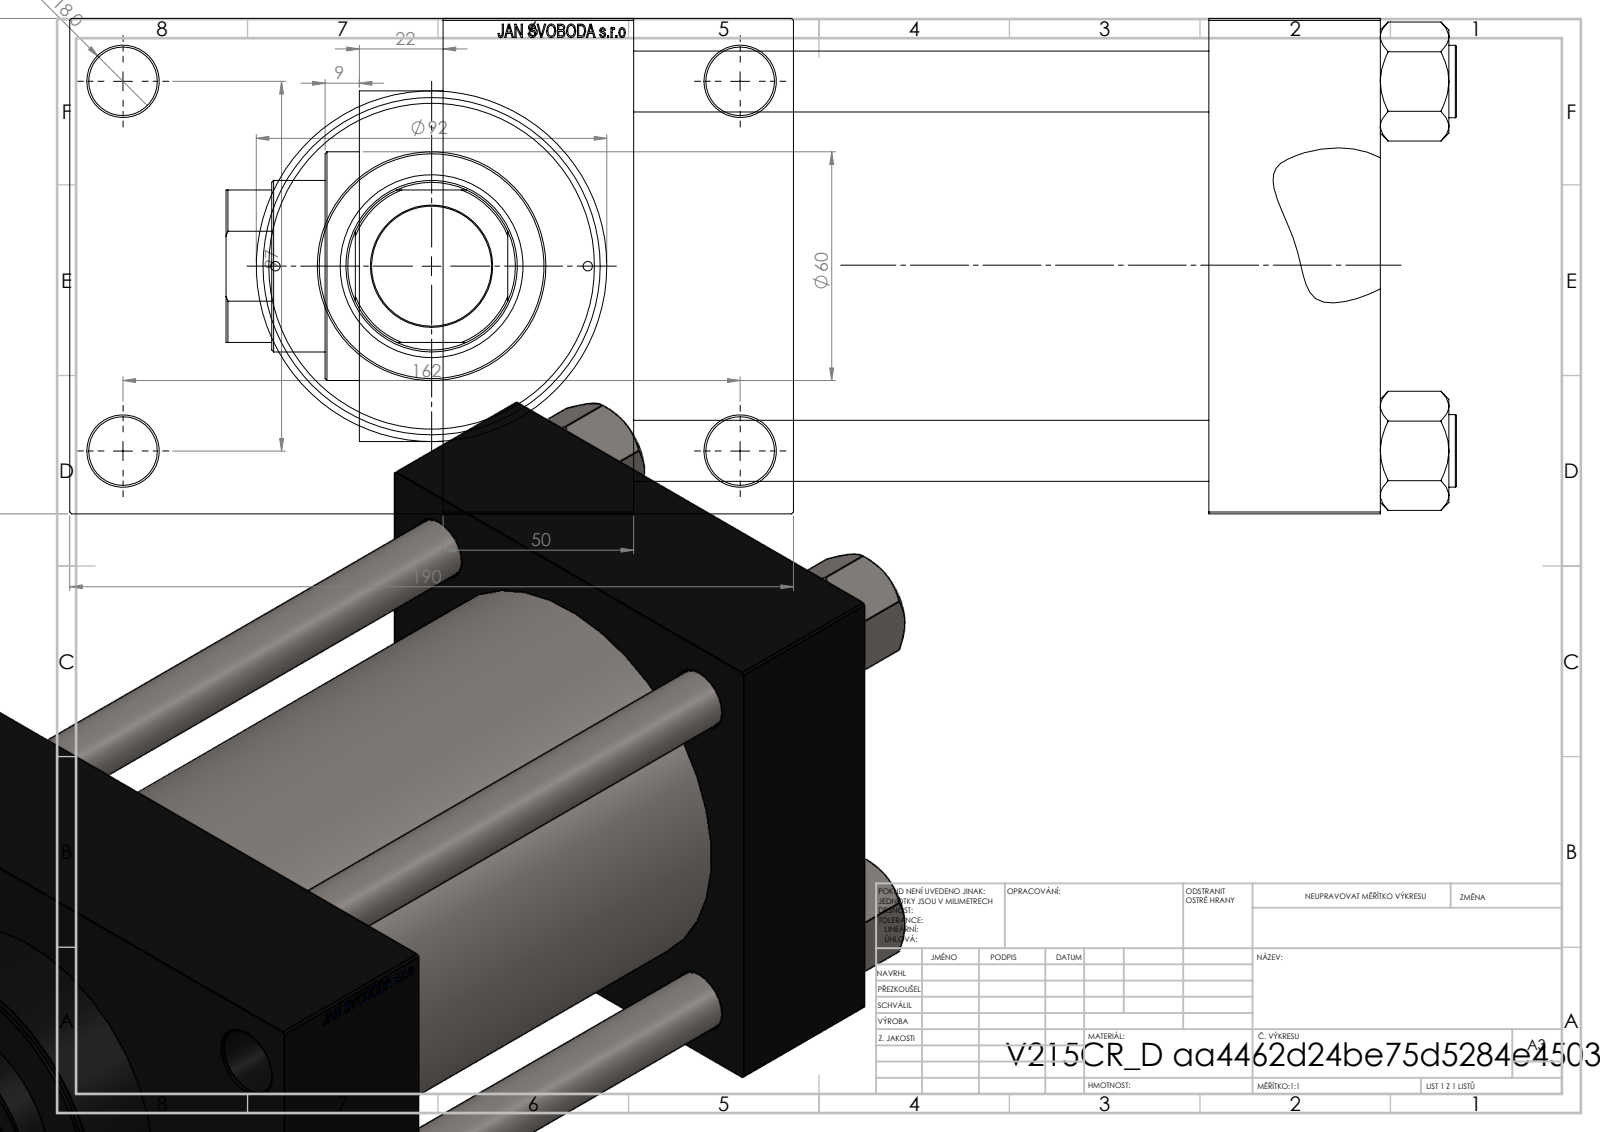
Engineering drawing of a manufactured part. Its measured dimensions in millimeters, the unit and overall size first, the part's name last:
Units: millimetres
Overall size (bounding box): 323 × 190 × 130
Round holes (diameter × count): ⌀16 ×4, ⌀18 ×4, ⌀2.5 ×2, ⌀7 ×2, ⌀26.44 ×2, ⌀35 ×2, ⌀31.5 ×1, ⌀45 ×1, ⌀48 ×1, ⌀76 ×1, ⌀85.5 ×1, ⌀100 ×1
Round bosses / shafts (diameter × count): ⌀19 ×4, ⌀106 ×1, ⌀92 ×1, ⌀60 ×1
Partial cylindrical surfaces — rounded edges, fillets, slot ends (radius × count): R22 ×1
Main face-to-face distances: 130, 45, 196, 151, 246, 201, 50, 30, 160, 96
Hole centre spacings: 32.55, 49.02, 62.87, 68.52, 94.41, 96.9, 101.73, 102.27
Volume: 2 859 000 mm³ · Surface area: 433 891 mm²
Bodies: 11 solids, 1159 faces (547 planar, 92 cylindrical, 520 other)
Part name (STEP PRODUCT): V215_VC_A; V215CR_VCP_D; V215CR_D_Body; V215CR_D_TYCINKA (+1 more)
STEP written by: SolidWorks 2019 (CONFIG_CONTROL_DESIGN)
